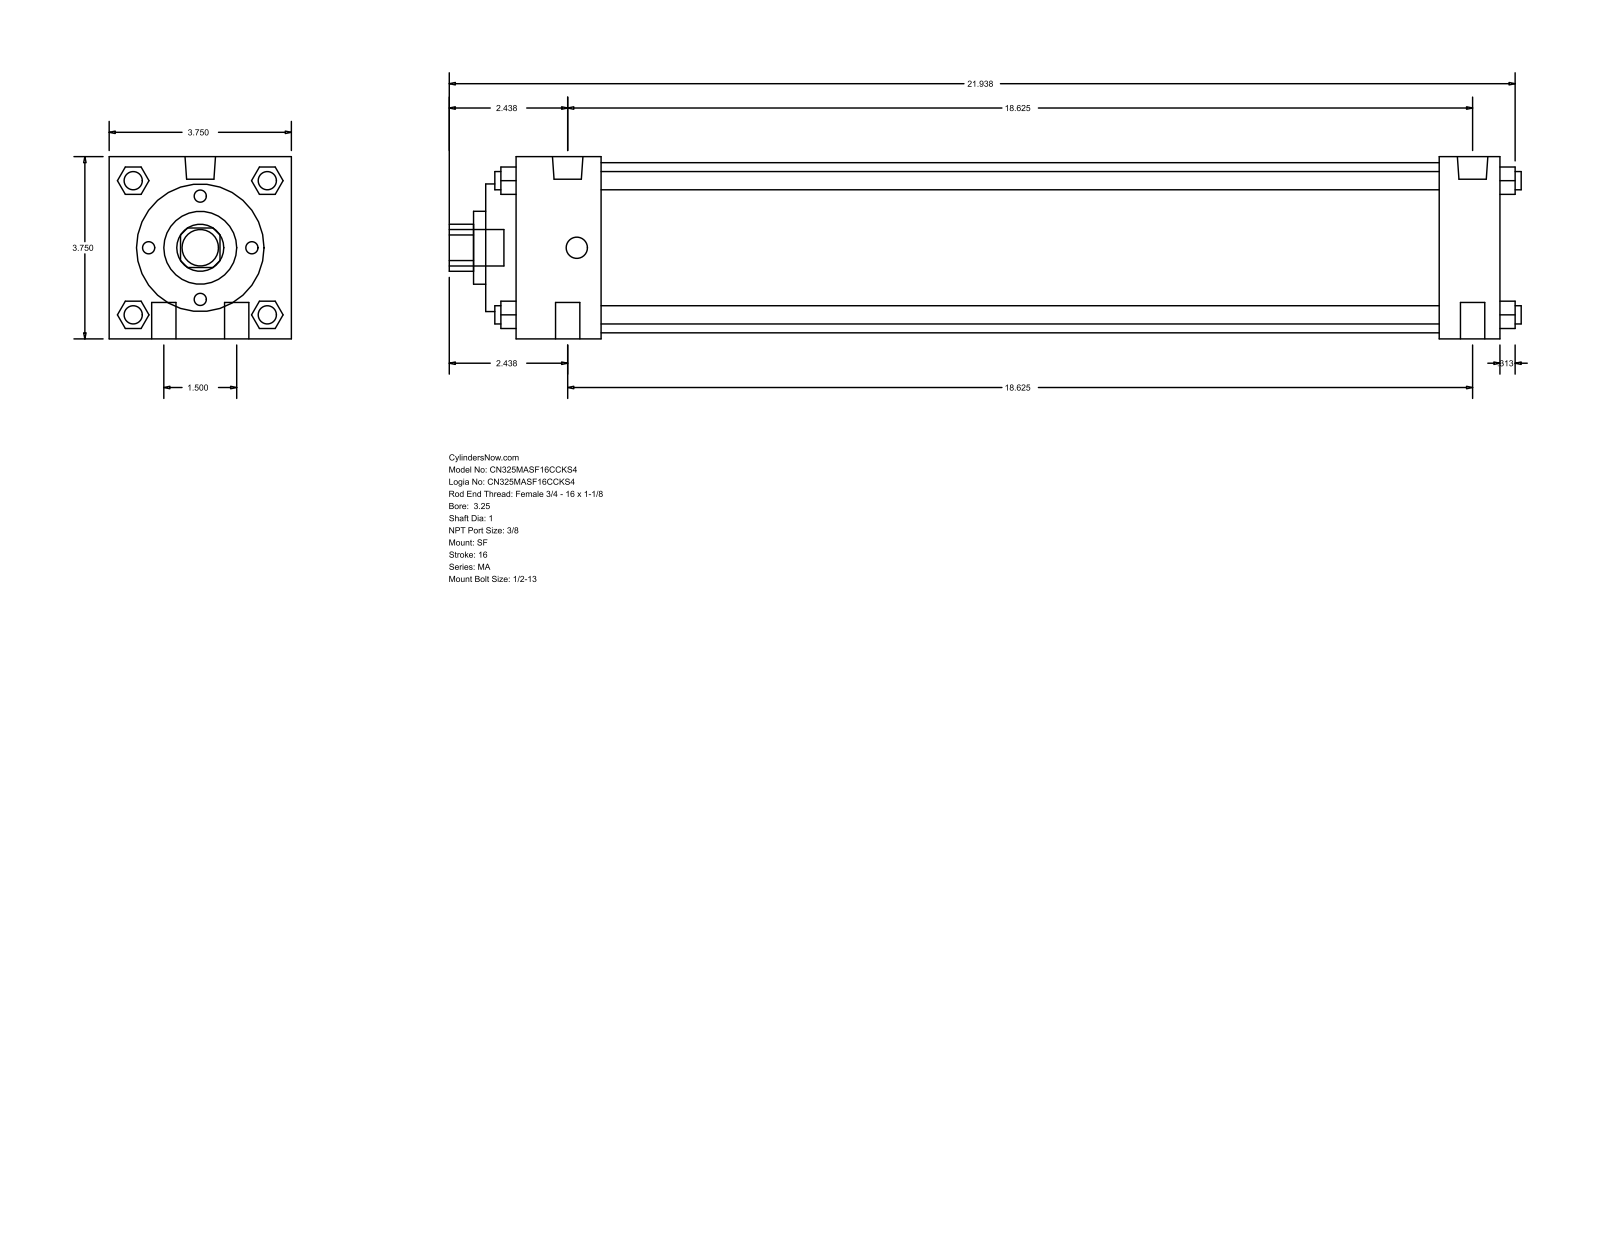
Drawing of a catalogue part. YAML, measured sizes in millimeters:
part_name: "MA_SF__0325_1"
step_written_by: "GSSL Pune (CONFIG_CONTROL_DESIGN)"
units: millimeters
bodies: {solids: 0, faces: 126, planar: 95, cylindrical: 31, other: 0}
overall_size: [560.39, 95.25, 95.25]
round_holes:
  - {diameter: 25.4, count: 1}
  - {diameter: 38.1, count: 1}
  - {diameter: 66.67, count: 1}
  - {diameter: 88.9, count: 1}
round_bosses_or_shafts:
  - {diameter: 12.7, count: 4}
  - {diameter: 9.53, count: 4}
  - {diameter: 15.93, count: 2}
  - {diameter: 11.11, count: 2}
  - {diameter: 19.05, count: 1}
partial_cylinders:
  - {radius: 12.29, count: 1}
face_to_face_distances: [95.24, 514.35, 530.22, 15.87, 482.6, 31.75, 44.46, 438.14, 469.89, 60.33]
